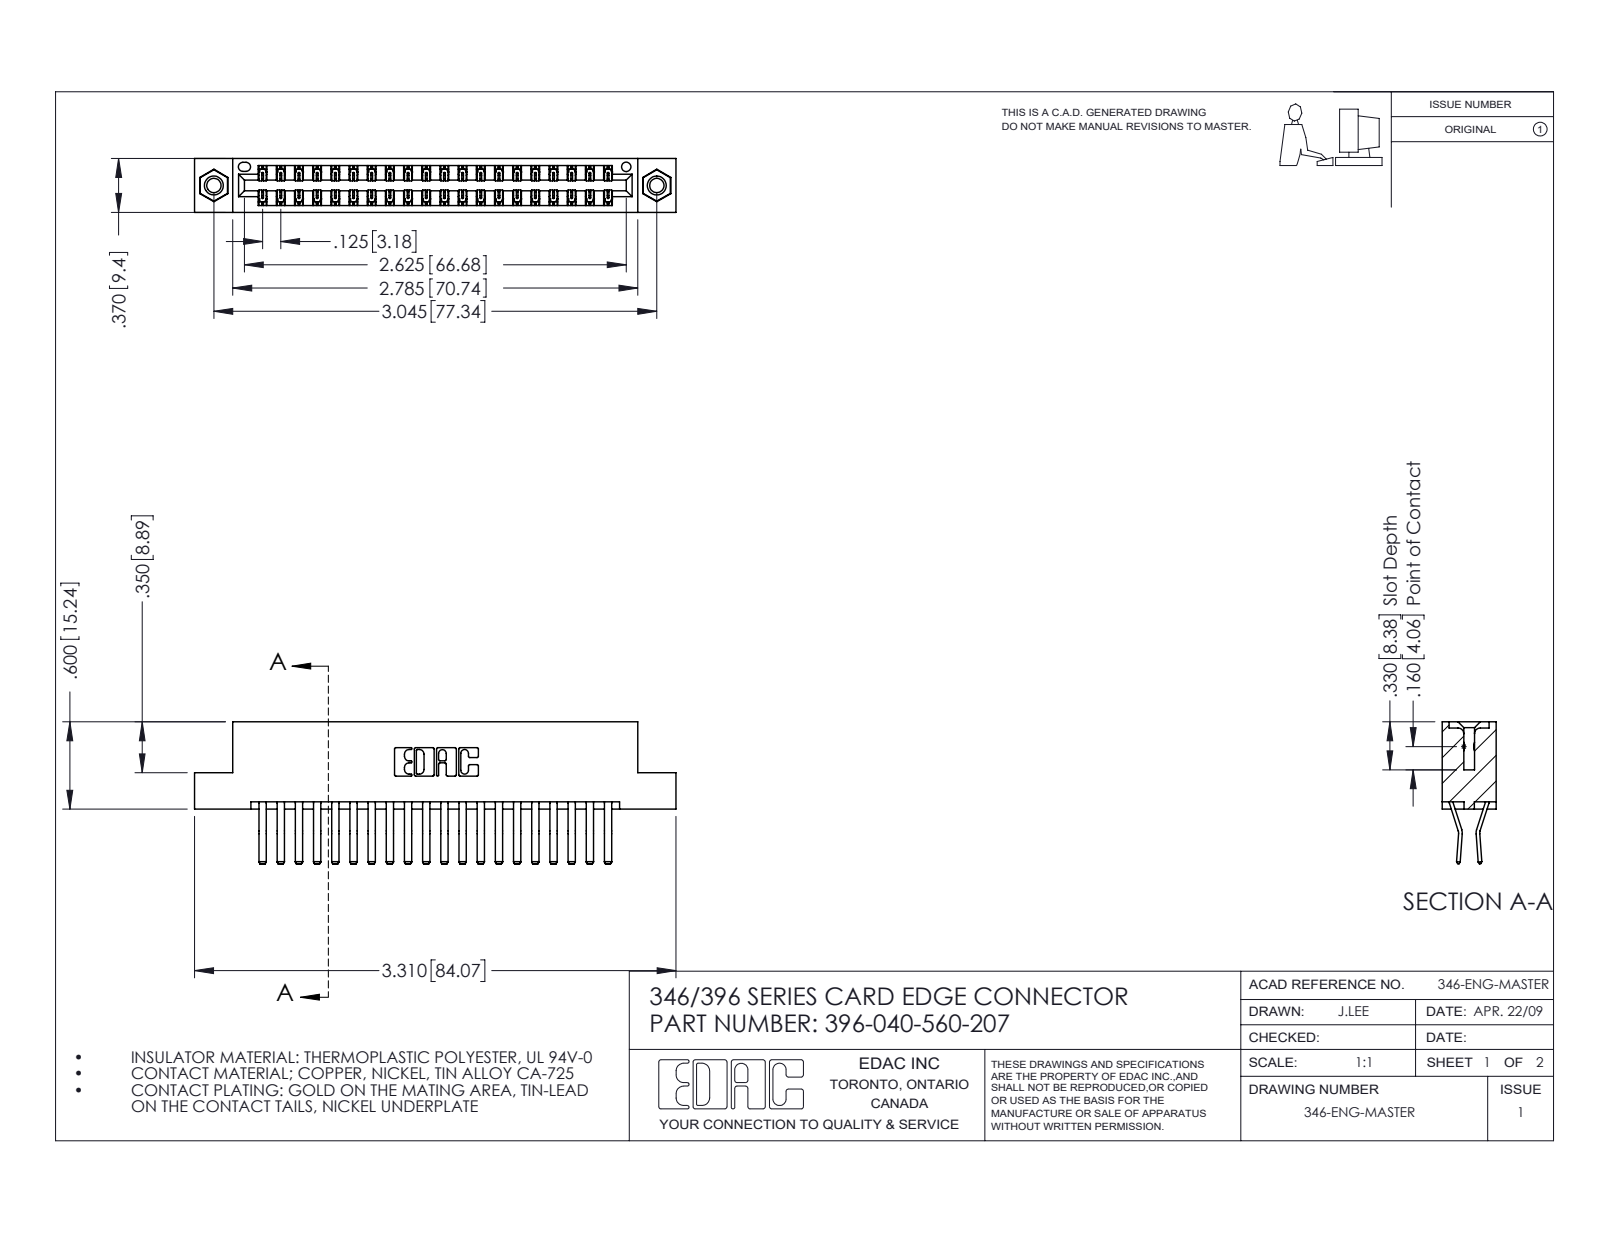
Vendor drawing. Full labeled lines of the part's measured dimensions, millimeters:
Part name (STEP PRODUCT): 345-250-001_345-250-005-103; 346 Part_Flush Mounting Lugs - 0.156 Dia-TI; 396-040-560-207; 345-292-001_560 Tail
STEP written by: SolidWorks 2016 (CONFIG_CONTROL_DESIGN)
Units: millimetres
Bodies: 43 solids, 2342 faces (1508 planar, 818 cylindrical, 16 other)
Overall size (bounding box): 84.1 × 24.8 × 9.4
Volume: 8 280 mm³ · Surface area: 11 760 mm²
Round holes (diameter × count): ⌀2.5 ×2, ⌀3.2 ×2, ⌀4 ×2, ⌀1.6 ×1
Round bosses / shafts (diameter × count): ⌀3.9 ×2
Partial cylindrical surfaces — rounded edges, fillets, slot ends (radius × count): R0.2 ×60, R0.3 ×22, R0.2 ×6, R0.8 ×6, R0.7 ×3, R0.3 ×2, R0.4 ×2, R0.6 ×2
Main face-to-face distances: 1.2, 8.2, 9.4, 6.4, 0.6, 1.8, 7.6, 7, 3.8, 5.6
Hole centre spacings: 6.2, 72.1, 77.3
